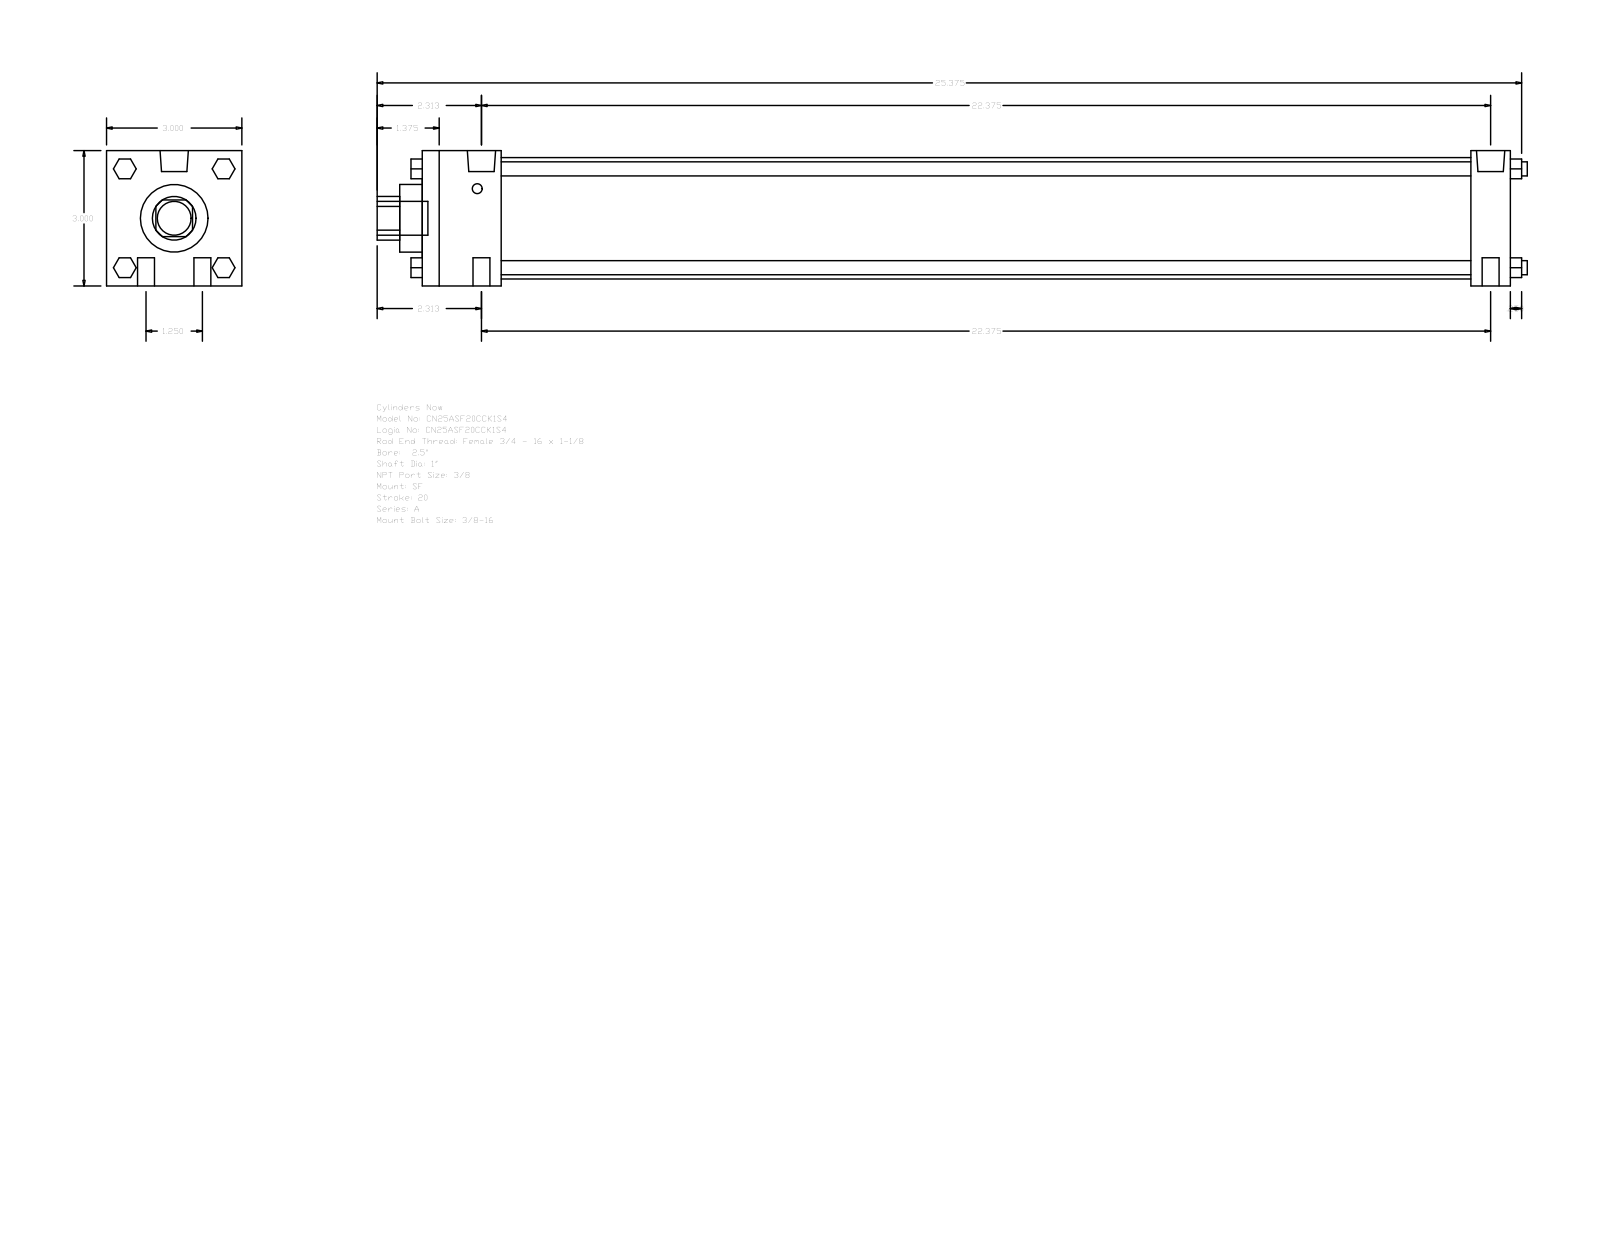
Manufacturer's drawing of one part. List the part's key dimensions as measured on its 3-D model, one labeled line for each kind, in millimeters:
Part name (STEP PRODUCT): A_SF__0250_1
STEP written by: GSSL Pune (CONFIG_CONTROL_DESIGN)
Units: millimetres
Bodies: 0 solids, 124 faces (94 planar, 30 cylindrical, 0 other)
Overall size (bounding box): 647.7 × 76.2 × 76.2
Round holes (diameter × count): ⌀25.4 ×1, ⌀38.1 ×1, ⌀68.33 ×1
Round bosses / shafts (diameter × count): ⌀9.53 ×4, ⌀7.94 ×4, ⌀15.93 ×2, ⌀5.56 ×2, ⌀19.05 ×1
Partial cylindrical surfaces — rounded edges, fillets, slot ends (radius × count): R12.29 ×1
Main face-to-face distances: 76.2, 612.77, 590.55, 22.22, 44.45, 546.1, 568.32, 12.7, 625.47, 6.35
